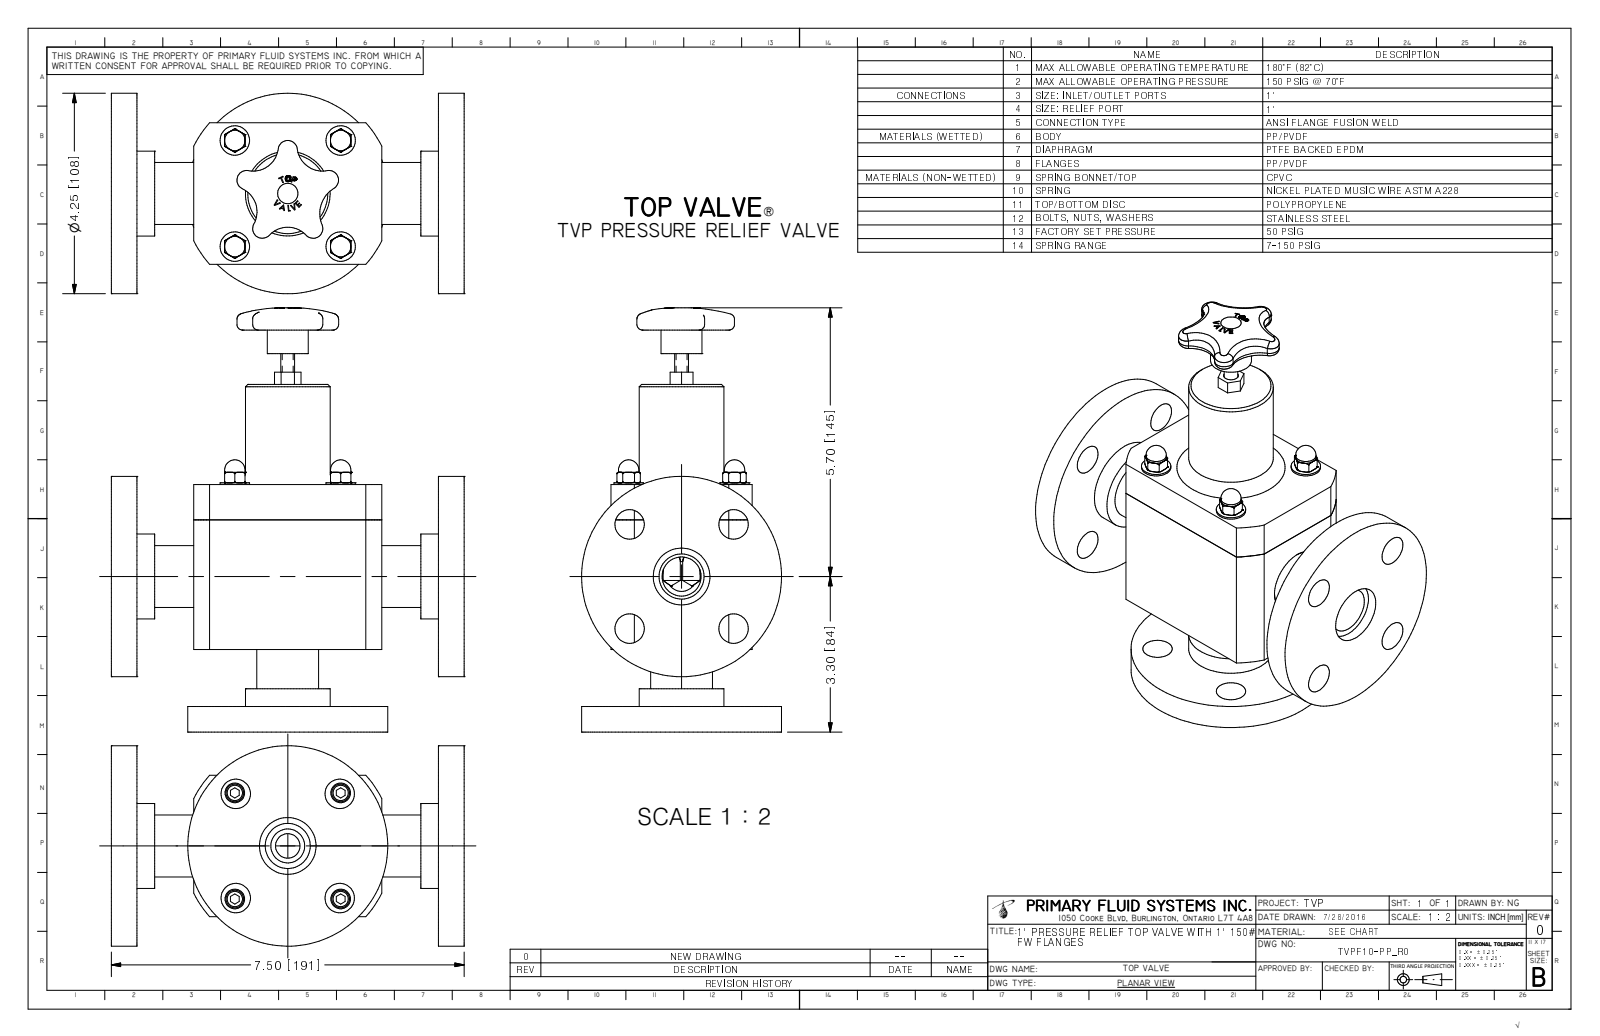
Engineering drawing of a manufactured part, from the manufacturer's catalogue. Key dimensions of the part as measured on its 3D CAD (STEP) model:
Part name (STEP PRODUCT): TVPF10-PP_R0
STEP written by: Autodesk Inventor 2009 (AUTOMOTIVE_DESIGN)
Units: inches
Bodies: 1 solid, 380 faces (159 planar, 72 cylindrical, 149 other)
Overall size (bounding box): 9 × 7.5 × 4.25
Volume: 69.51 in³ · Surface area: 243.4 in²
Round holes (diameter × count): ⌀0.625 ×8, ⌀0.175 ×4, ⌀0.957 ×2, ⌀1.205 ×2, ⌀2.525 ×1
Round bosses / shafts (diameter × count): ⌀0.625 ×4, ⌀0.433 ×4, ⌀0.375 ×4, ⌀4.25 ×2, ⌀1.8 ×2, ⌀1.315 ×2, ⌀2.5 ×1, ⌀0.87 ×1
Partial cylindrical surfaces — rounded edges, fillets, slot ends (radius × count): R0.085 ×5, R0.205 ×5, R0.536 ×4, R0.656 ×4, R0.625 ×1, R0.745 ×1, R2.238 ×1
Main face-to-face distances: 0.545, 6.955, 1.75, 1.205, 7.5, 3, 5.75, 5.205, 6.41, 5.25
Hole centre spacings: 1.562, 2.209, 2.23, 2.23, 2.25, 3.125, 3.153, 0.029
